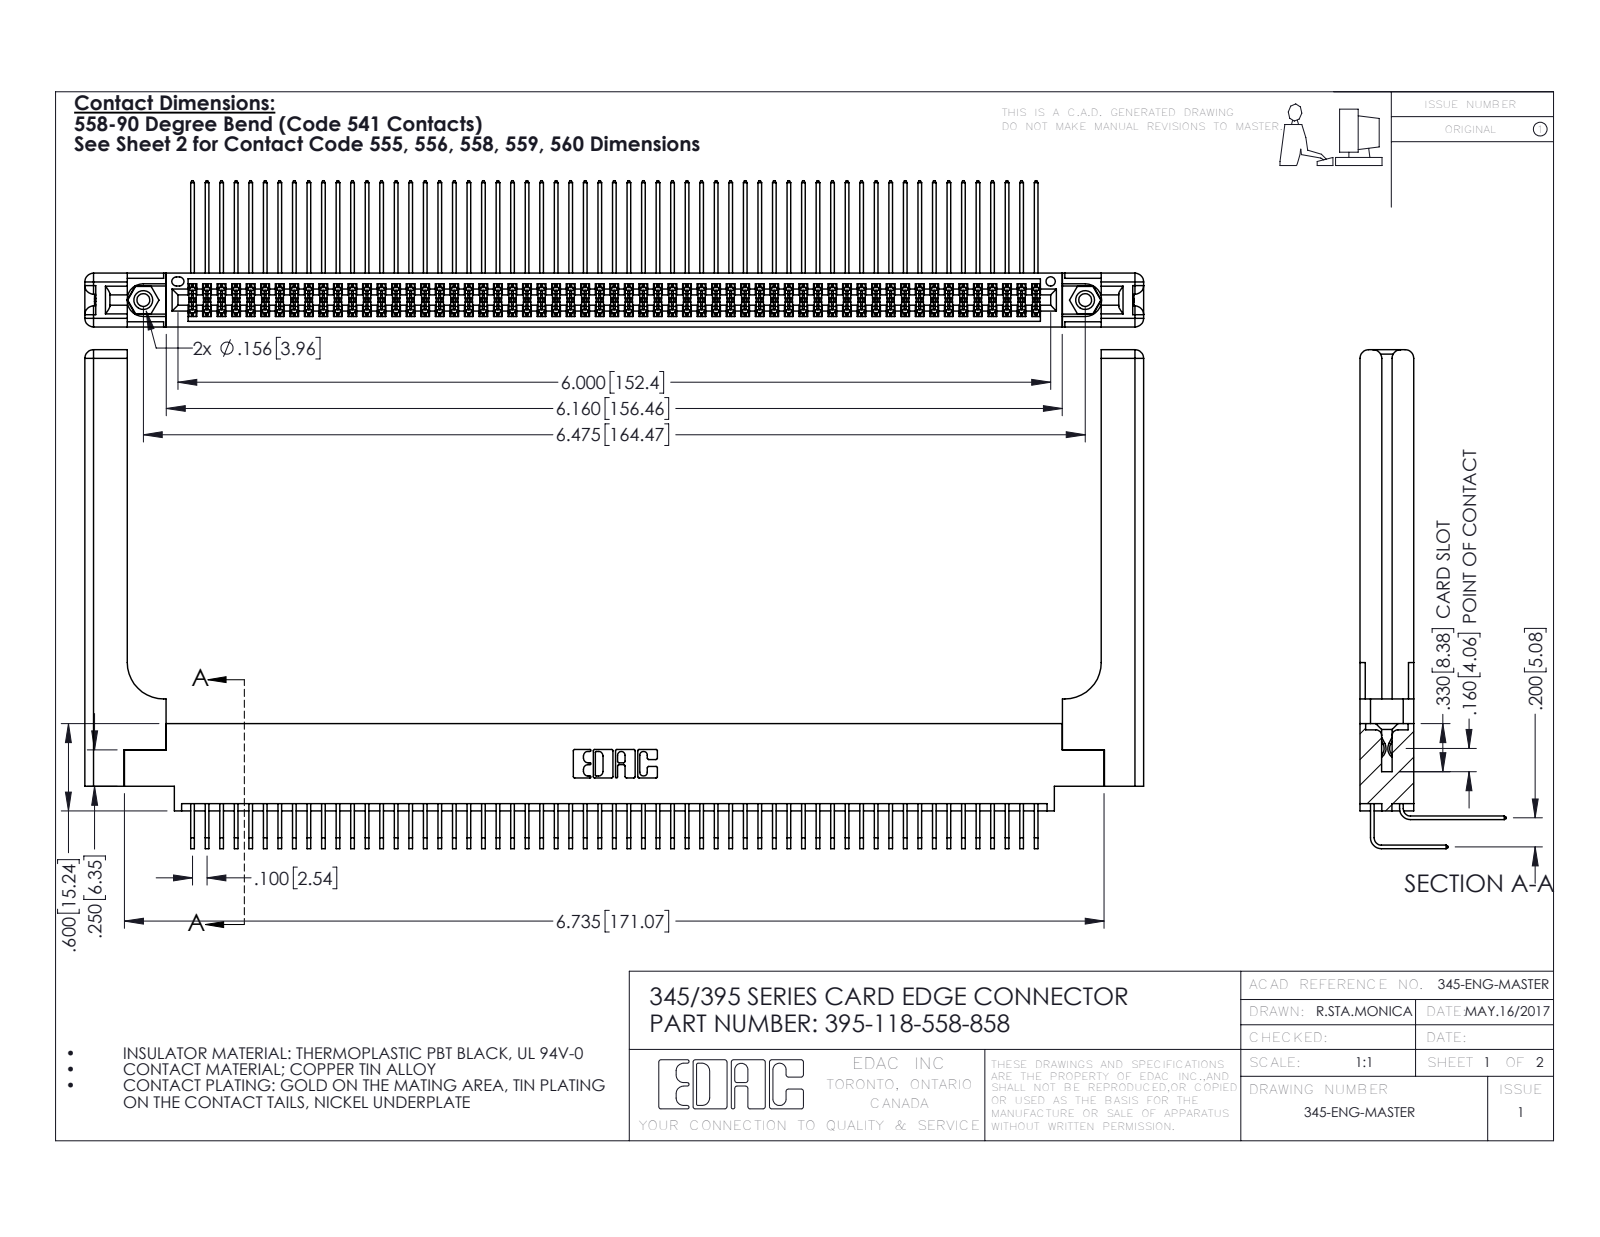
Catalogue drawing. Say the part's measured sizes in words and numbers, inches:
The part is named "345-292-001_558 Tail - 2; 345-220-058_345-220-058; 395-118-558-858; 345 Part_0.170 Offset - 0.156 Dia-TH (+2 more)". Its 3-D file was written by "SolidWorks 2016 (CONFIG_CONTROL_DESIGN)". It is 123 solids with 6522 faces: 4362 planar, 2100 cylindrical and 60 other. Overall it measures 7.279 by 3.429 by 1.005 inches. Its volume is 1.657 cubic inches and its surface area 56.35 square inches. Round holes: 2 of diameter 0.089, 2 of diameter 0.125, 2 of diameter 0.156, 1 of diameter 0.064. Round bosses or shafts: 2 of diameter 0.155. Partial cylindrical surfaces (rounded edges, fillets, slot ends): 178 of radius 0.006, 22 of radius 0.01, 16 of radius 0.06, 6 of radius 0.007, 6 of radius 0.031, 3 of radius 0.026, 2 of radius 0.014, 2 of radius 0.019. The main face-to-face distances are 0.072, 0.298, 0.37, 0.2, 0.098, 0.272, 0.025, 0.225, 0.175, 0.148. The hole center spacings are 0.27, 6.239, 6.475.
